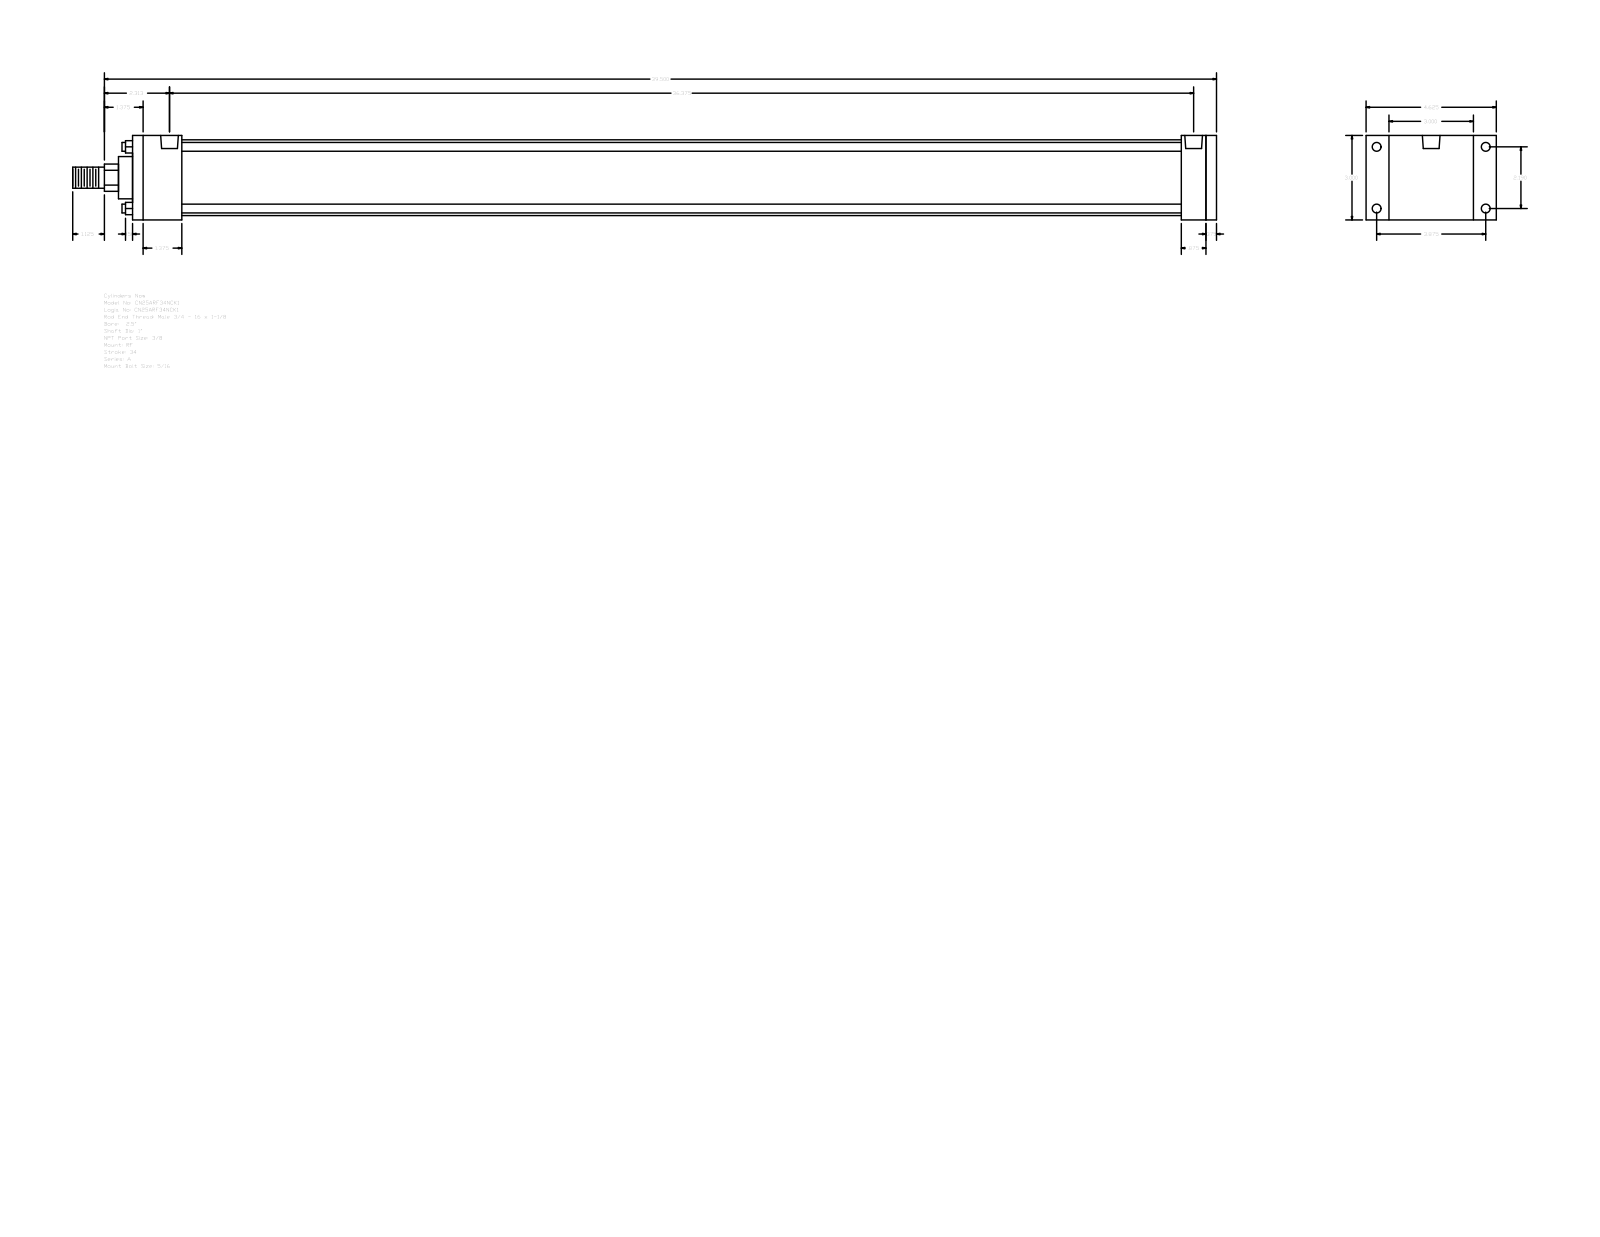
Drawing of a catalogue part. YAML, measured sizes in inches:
part_name: "A_RF__0250_1"
step_written_by: "GSSL Pune (CONFIG_CONTROL_DESIGN)"
units: inches
bodies: {solids: 0, faces: 92, planar: 64, cylindrical: 28, other: 0}
overall_size: [40.625, 4.625, 3]
round_holes:
  - {diameter: 0.219, count: 4}
  - {diameter: 0.313, count: 4}
  - {diameter: 0.627, count: 2}
round_bosses_or_shafts:
  - {diameter: 0.313, count: 4}
  - {diameter: 2.69, count: 1}
  - {diameter: 1.5, count: 1}
  - {diameter: 1, count: 1}
  - {diameter: 0.75, count: 1}
partial_cylinders:
  - {radius: 0.484, count: 1}
face_to_face_distances: [3, 38.5, 0.375, 38.125, 1.75, 37.25, 35.5, 36.375, 36.75, 0.875]
hole_center_spacings: [0.094, 2.19, 3.875, 4.451, 36.469, 36.562, 36.375]
